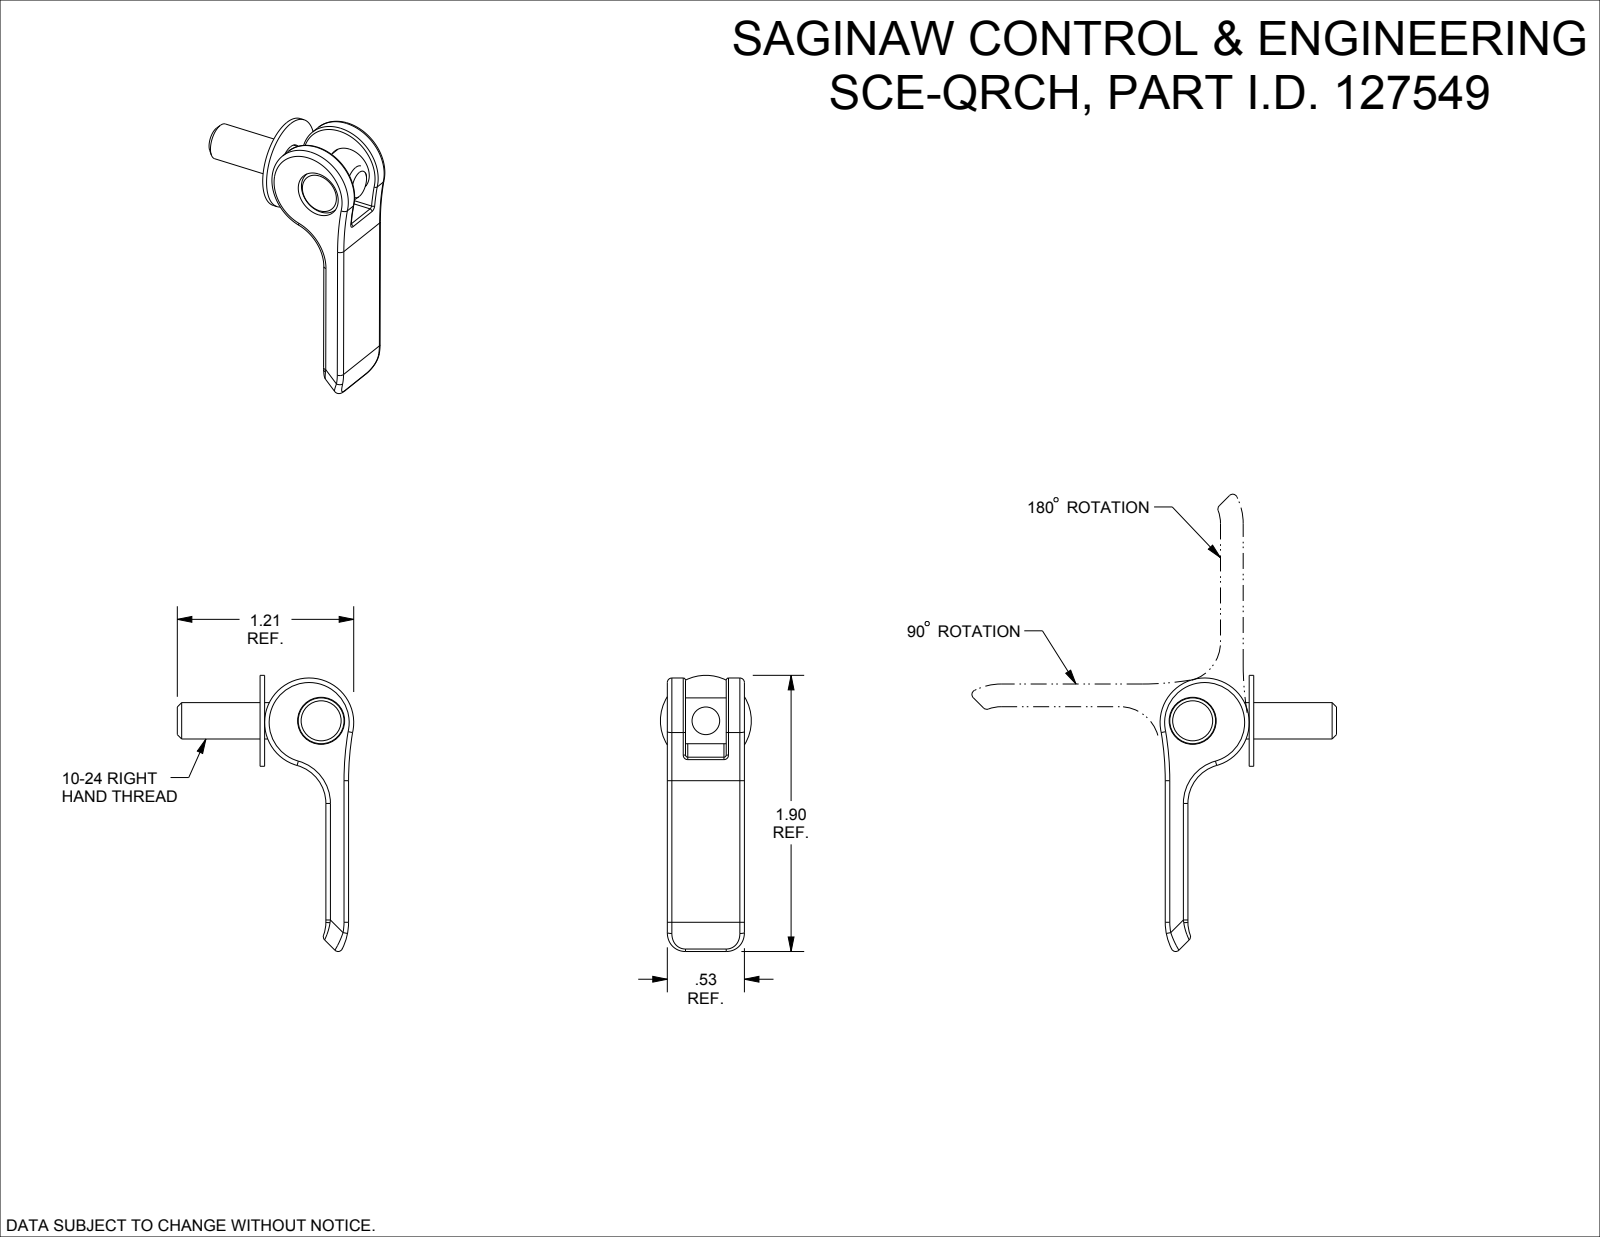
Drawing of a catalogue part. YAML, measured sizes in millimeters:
part_name: "SCE-QRCH"
step_written_by: "SolidWorks 2019 (CONFIG_CONTROL_DESIGN)"
units: millimeters
bodies: {solids: 4, faces: 77, planar: 15, cylindrical: 28, other: 34}
overall_size: [48.2, 30.8, 15.9]
volume: 4410
surface_area: 3683
round_holes:
  - {diameter: 5.1, count: 1}
  - {diameter: 6.6, count: 1}
  - {diameter: 8.2, count: 1}
round_bosses_or_shafts:
  - {diameter: 15.9, count: 1}
  - {diameter: 8, count: 1}
  - {diameter: 6.4, count: 1}
partial_cylinders:
  - {radius: 0.4, count: 7}
  - {radius: 0.8, count: 6}
  - {radius: 3.2, count: 2}
  - {radius: 6.4, count: 2}
  - {radius: 6.9, count: 1}
  - {radius: 7.8, count: 1}
  - {radius: 10.3, count: 1}
  - {radius: 50.8, count: 1}
face_to_face_distances: [4, 3.2, 10.3, 13.5, 0.8, 11.5, 15.4, 10.7, 14.7, 7.1]
